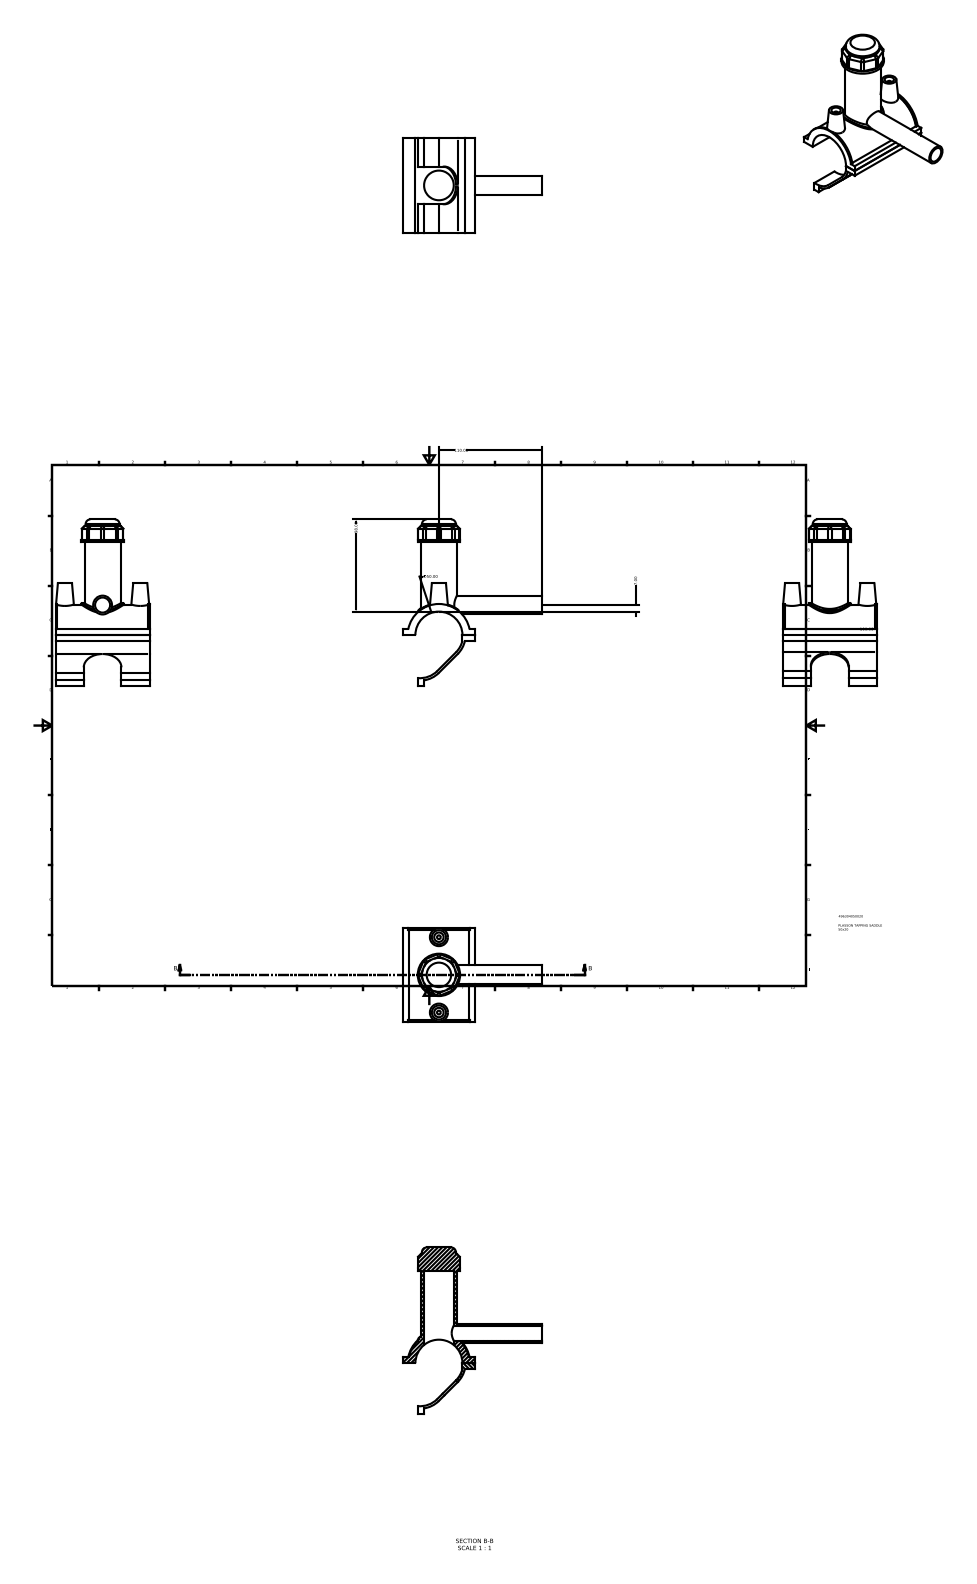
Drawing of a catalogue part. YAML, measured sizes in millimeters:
part_name: "496304050020"
step_written_by: "Autodesk Inventor 2015 (AUTOMOTIVE_DESIGN)"
units: millimeters
bodies: {solids: 2, faces: 111, planar: 66, cylindrical: 32, other: 13}
overall_size: [177.37, 148, 100]
volume: 167111
surface_area: 71399
round_holes:
  - {diameter: 10, count: 2}
  - {diameter: 16, count: 1}
  - {diameter: 31.5, count: 1}
round_bosses_or_shafts:
  - {diameter: 4, count: 2}
  - {diameter: 45, count: 1}
  - {diameter: 38.25, count: 1}
  - {diameter: 36, count: 1}
  - {diameter: 20, count: 1}
partial_cylinders:
  - {radius: 5, count: 8}
  - {radius: 25.68, count: 2}
  - {radius: 28.28, count: 2}
  - {radius: 20, count: 1}
  - {radius: 21.38, count: 1}
  - {radius: 25, count: 1}
  - {radius: 32.5, count: 1}
  - {radius: 33.15, count: 1}
face_to_face_distances: [6.2, 2.6, 98.45, 92.25, 100, 12.4, 104.65, 76, 41.58, 63]
hole_center_spacings: [40, 80]
